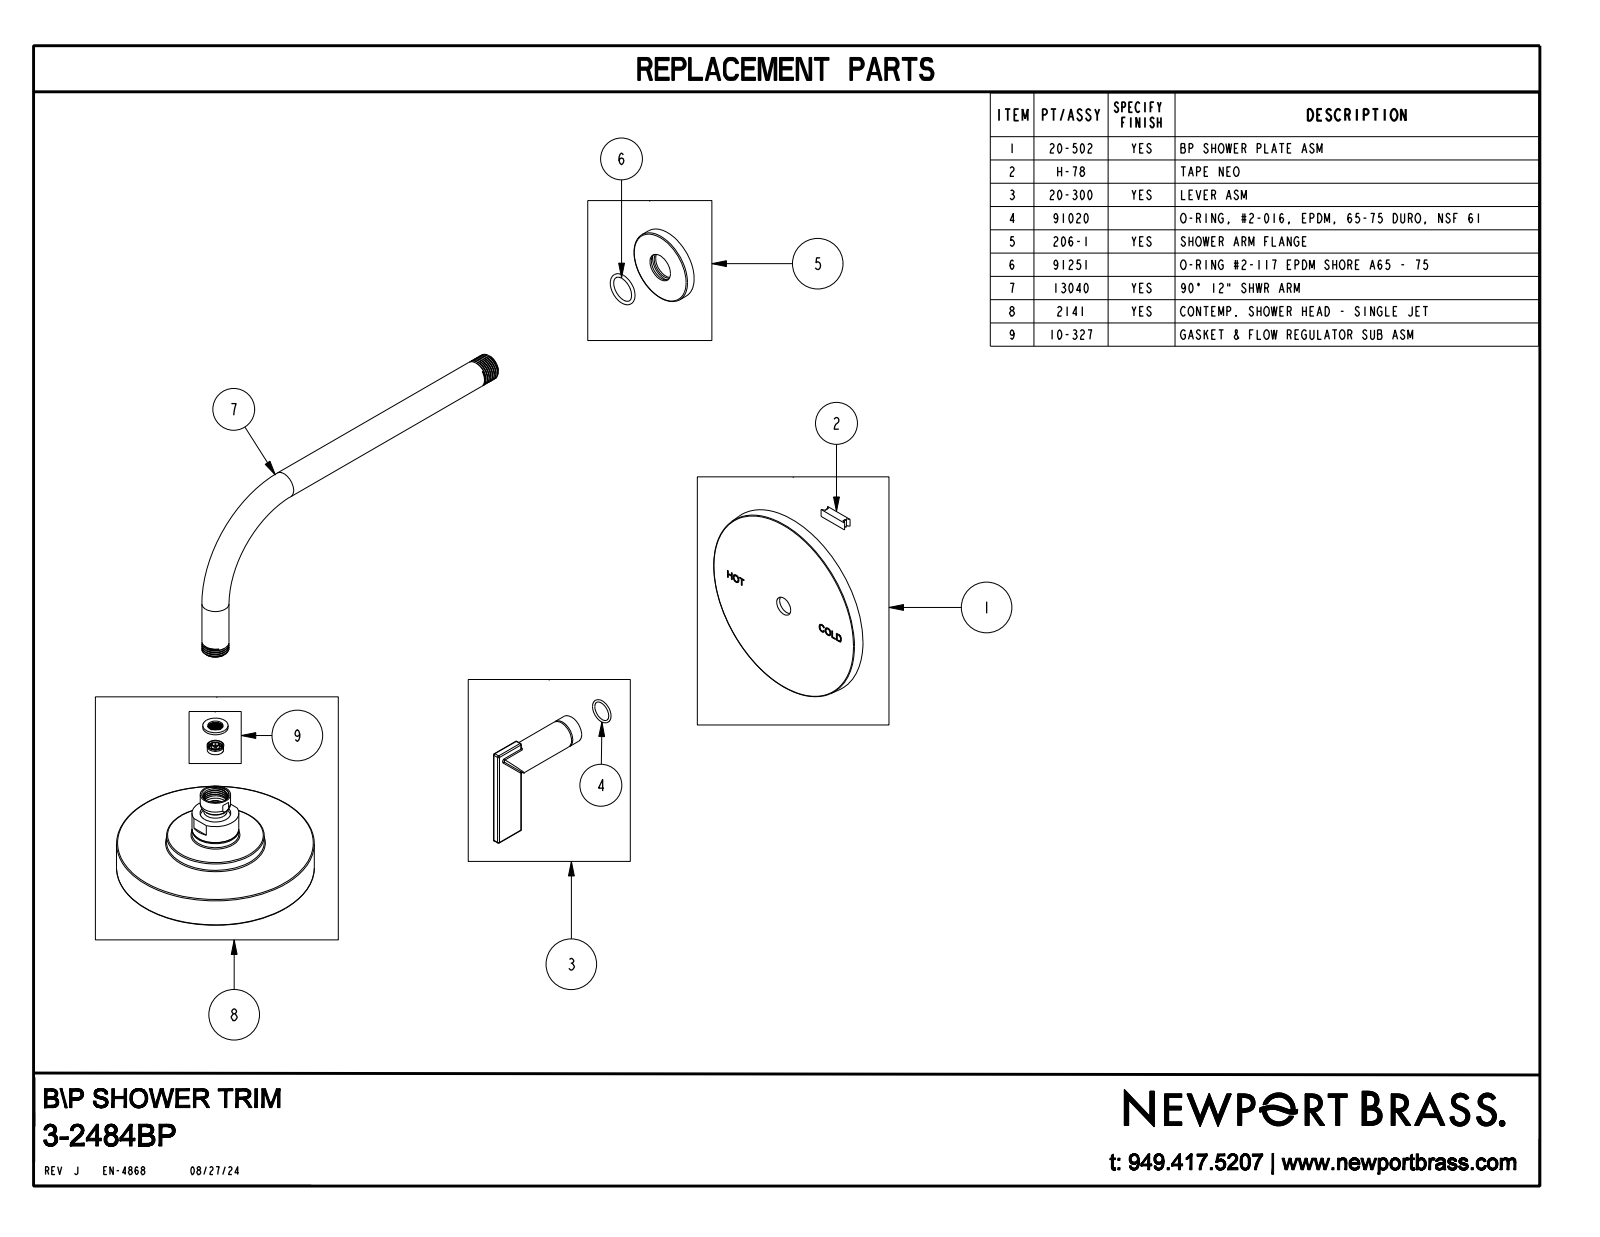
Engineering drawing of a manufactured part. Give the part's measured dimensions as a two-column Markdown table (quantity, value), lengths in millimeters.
| quantity | value |
| --- | --- |
| part name | 3-248BP |
| STEP written by | CREO PARAMETRIC BY PTC INC, 2018400 (CONFIG_CONTROL_DESIGN) |
| units | millimeters |
| bodies | 2 solids, 1027 faces (163 planar, 226 cylindrical, 638 other) |
| overall size | 485.8 × 350.5 × 152.4 |
| volume | 895 200 mm³ |
| surface area | 134 600 mm² |
| round holes (diameter × count) | 1.3 × 90, 5.6 × 1, 133.5 × 1 |
| round bosses / shafts (diameter × count) | 20.7 × 2, 150.1 × 1, 132.6 × 1, 74.2 × 1, 57.2 × 1, 35.6 × 1, 23 × 1, 21.8 × 1 |
| partial cylindrical surfaces (radius × count) | 1 × 16 |
| main face-to-face distances | 8.9, 7.4, 7.9, 1, 6, 27.5, 20.1, 90.2, 82.3, 81.3 |
| hole center spacings | 24.9, 35.8, 14, 21.6, 48.1, 10.9, 12.1, 23.2 |
